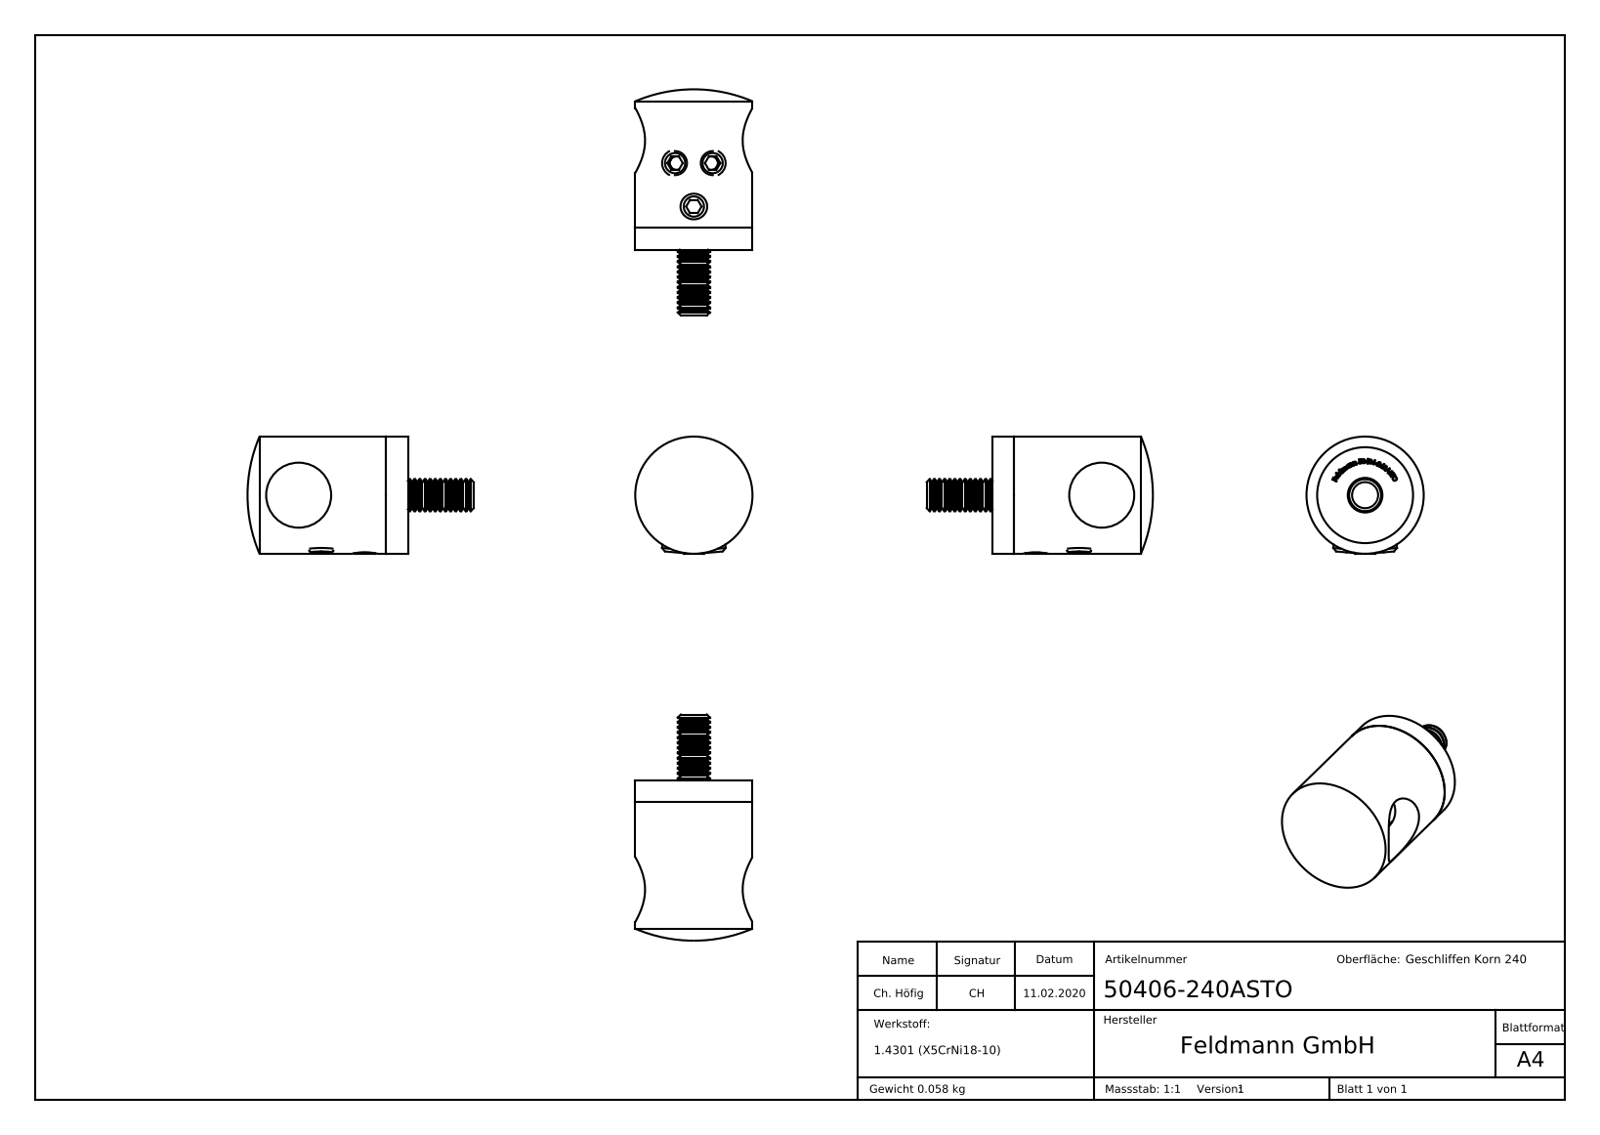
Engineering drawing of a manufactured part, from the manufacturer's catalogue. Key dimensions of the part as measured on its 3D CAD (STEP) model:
Part name (STEP PRODUCT): DIN914_DIN 914 M5x6; Querstabhalter Teil2 Konfig; Querstabhalter Teil1 Konfig_50XXX-240ASTO Teil1 12,2; DIN913 (+7 more)
STEP written by: SolidWorks 2015 (CONFIG_CONTROL_DESIGN)
Units: millimetres
Bodies: 6 solids, 428 faces (208 planar, 37 cylindrical, 183 other)
Overall size (bounding box): 69790.35 × 11012.2 × 5000
Volume: 7 943 mm³ · Surface area: 6 097 mm²
Round holes (diameter × count): ⌀4.2 ×3, ⌀6.5 ×1, ⌀12 ×1, ⌀12.2 ×1, ⌀18 ×1
Round bosses / shafts (diameter × count): ⌀5 ×3, ⌀22 ×1, ⌀11.9 ×1, ⌀11.57 ×1, ⌀6 ×1
Main face-to-face distances: 2.1, 2, 4.1, 10.65, 12.65, 8.55, 2.5, 11.6, 9.6, 7.5
